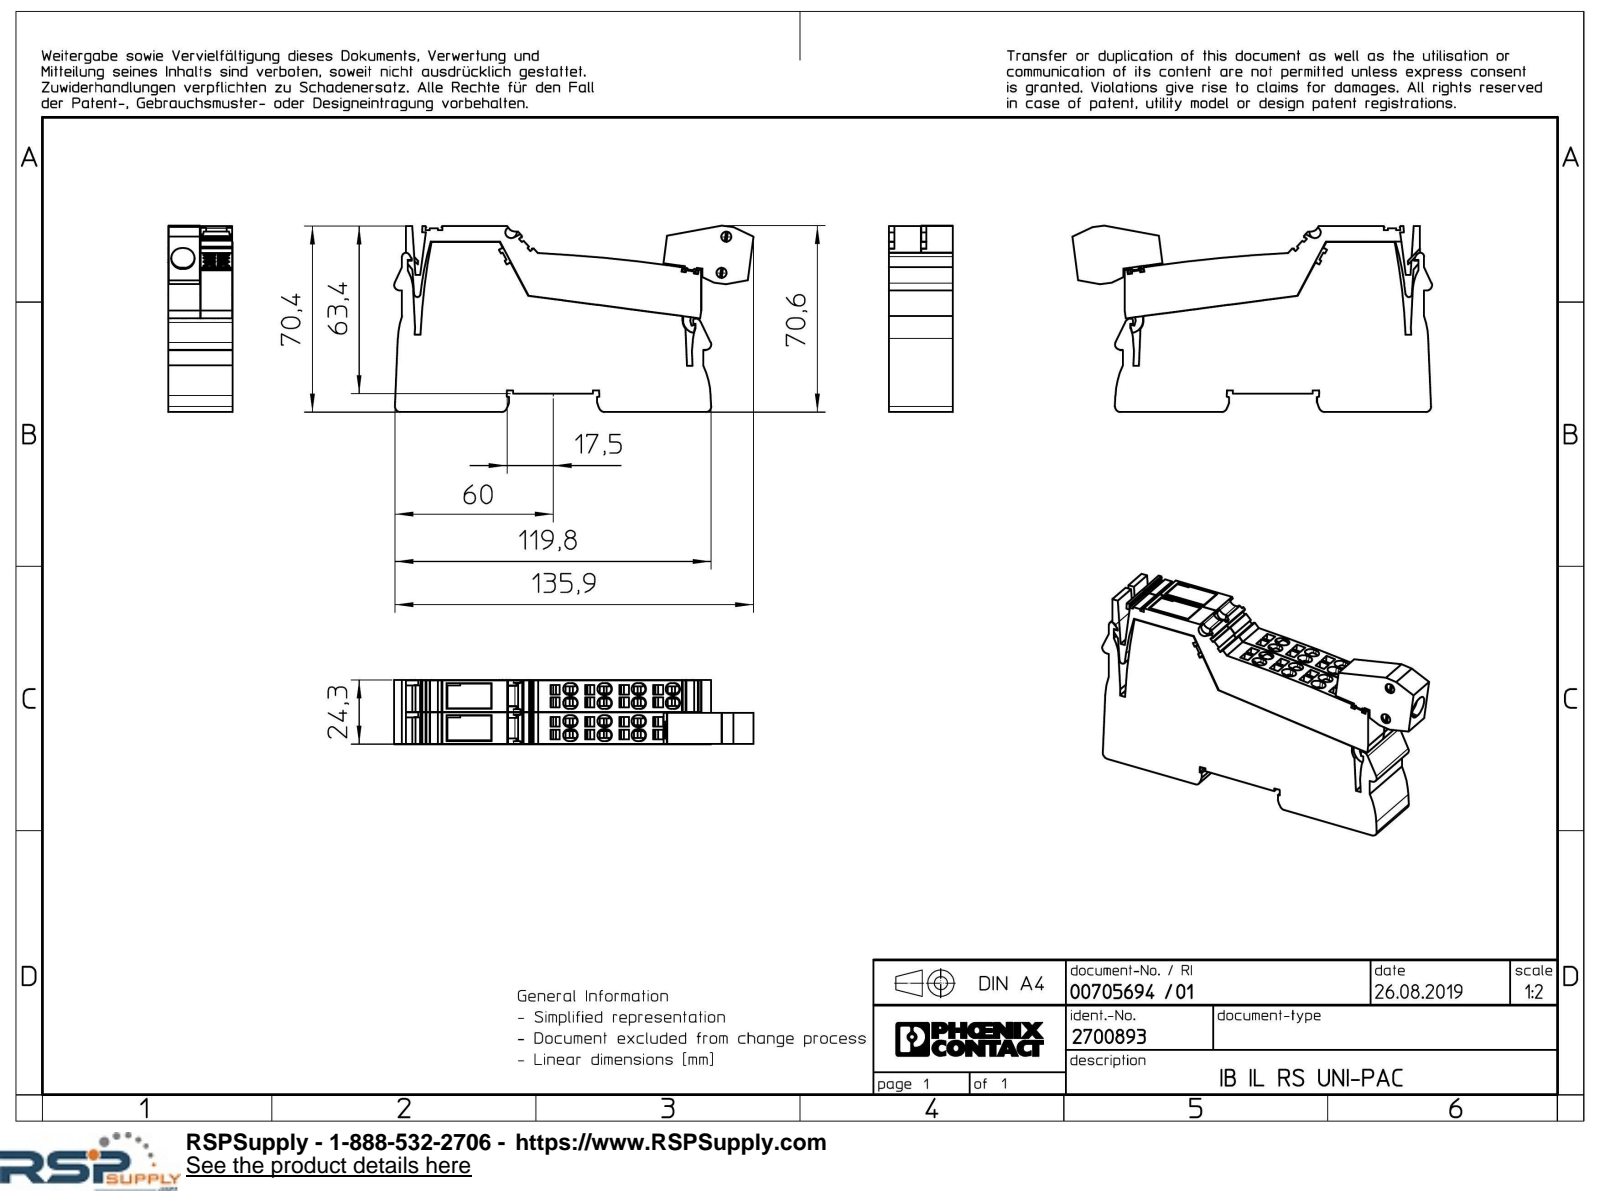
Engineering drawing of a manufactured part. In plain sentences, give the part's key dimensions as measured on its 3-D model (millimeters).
The part is named "L_L_KGG_GN_6021-select; L-L_ST_GN_6021-select; L_L_4_GEH_GN_6021-select; L_L_LWL_OG_HKS_7K_AUSSEN-select (+1 more)". Its 3-D file was written by "Creo Elements/Direct Modeling 20.1A 29-Sep-2018 (C) Parametric Technology GmbH (AUTOMOTIVE_DESIGN)". It is 6 solids with 1169 faces: 993 planar, 120 cylindrical and 56 other. Overall it measures 136.17 by 70.58 by 24.3 millimeters. Its volume is 165 873 cubic millimeters and its surface area 49 712 square millimeters. Round holes: 12 of diameter 1.2, 2 of diameter 3.83. Partial cylindrical surfaces (rounded edges, fillets, slot ends): 32 of radius 2.25, 6 of radius 2, 4 of radius 0.5, 4 of radius 0.6, 2 of radius 0.15, 2 of radius 0.2, 2 of radius 2.1, 2 of radius 2.6. The main face-to-face distances are 24.3, 12.15, 12, 12.1, 24.2, 12.2, 24.25, 12.25, 12.05, 24.15. The hole center spacings are 13, 13.86, 17.8, 4.8, 12.15, 14.94, 21.36, 26.
